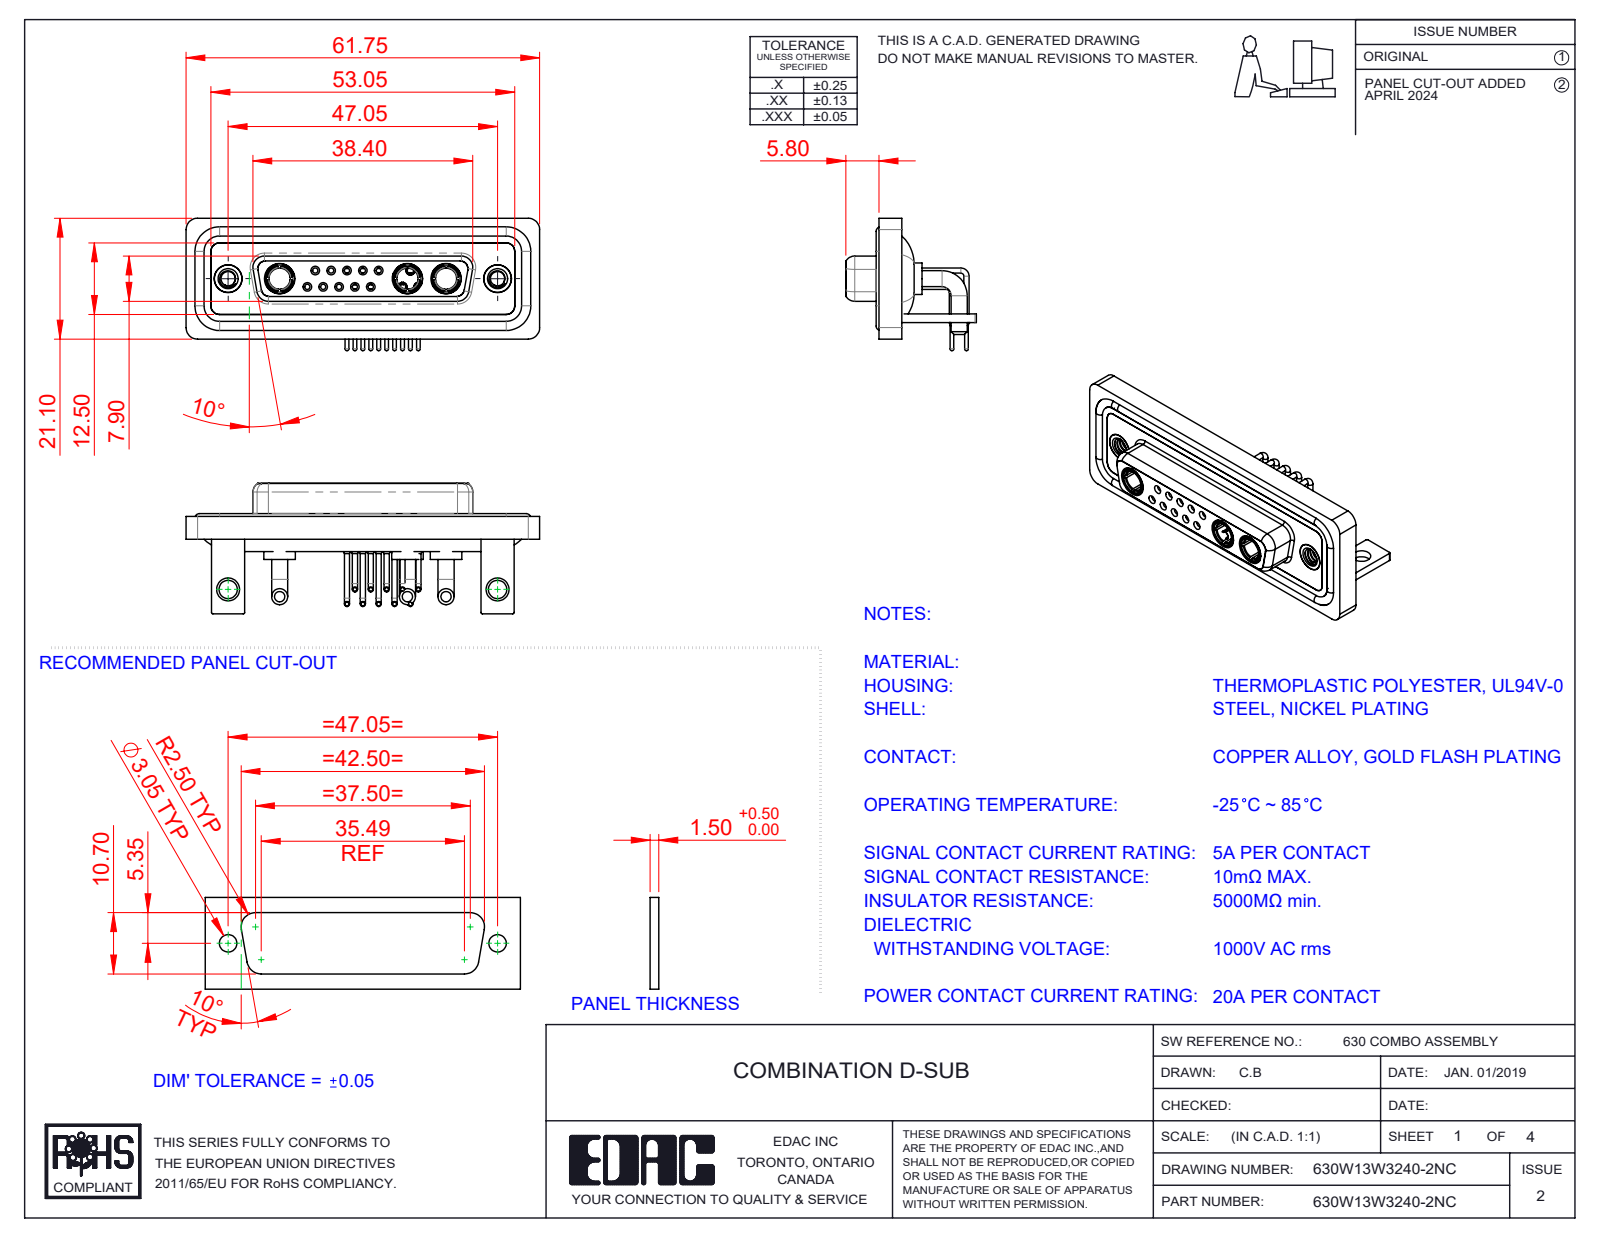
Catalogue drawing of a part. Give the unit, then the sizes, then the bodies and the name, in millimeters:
Units: millimetres
Overall size (bounding box): 61.75 × 23.12 × 22.8
Round holes (diameter × count): ⌀0.9 ×10, ⌀1.1 ×10, ⌀1.5 ×10, ⌀2 ×10, ⌀1.6 ×5, ⌀1.7 ×5, ⌀4.85 ×5, ⌀3.7 ×3, ⌀5.3 ×3, ⌀2.5 ×2, ⌀3.2 ×2, ⌀4 ×2
Round bosses / shafts (diameter × count): ⌀0.9 ×15, ⌀1.6 ×12, ⌀0.65 ×10, ⌀2.8 ×6, ⌀2 ×5, ⌀1.5 ×5, ⌀5.5 ×3, ⌀5.2 ×3
Partial cylindrical surfaces — rounded edges, fillets, slot ends (radius × count): R2 ×19, R1.5 ×18, R0.25 ×16, R1.35 ×8, R1.6 ×8, R0.5 ×5, R0.6 ×4, R0.65 ×4
Main face-to-face distances: 0.4, 1.8, 2.9, 3.7, 1.5, 4.1, 1.1, 1.4, 1.6, 3.1
Hole centre spacings: 3.16, 2.77, 5.54, 5.04, 8.31, 5.03, 7.49, 11.08
Volume: 8 830 mm³ · Surface area: 15 035 mm²
Bodies: 25 solids, 1192 faces (362 planar, 515 cylindrical, 315 other)
Part name (STEP PRODUCT): 630Combo Housing_13W3; 630Combo Stabilizer Bracket_50 Contacts; Power Socket_20A RA; 630W13W3140-2NC (+6 more)
STEP written by: SolidWorks 2023 (CONFIG_CONTROL_DESIGN)
